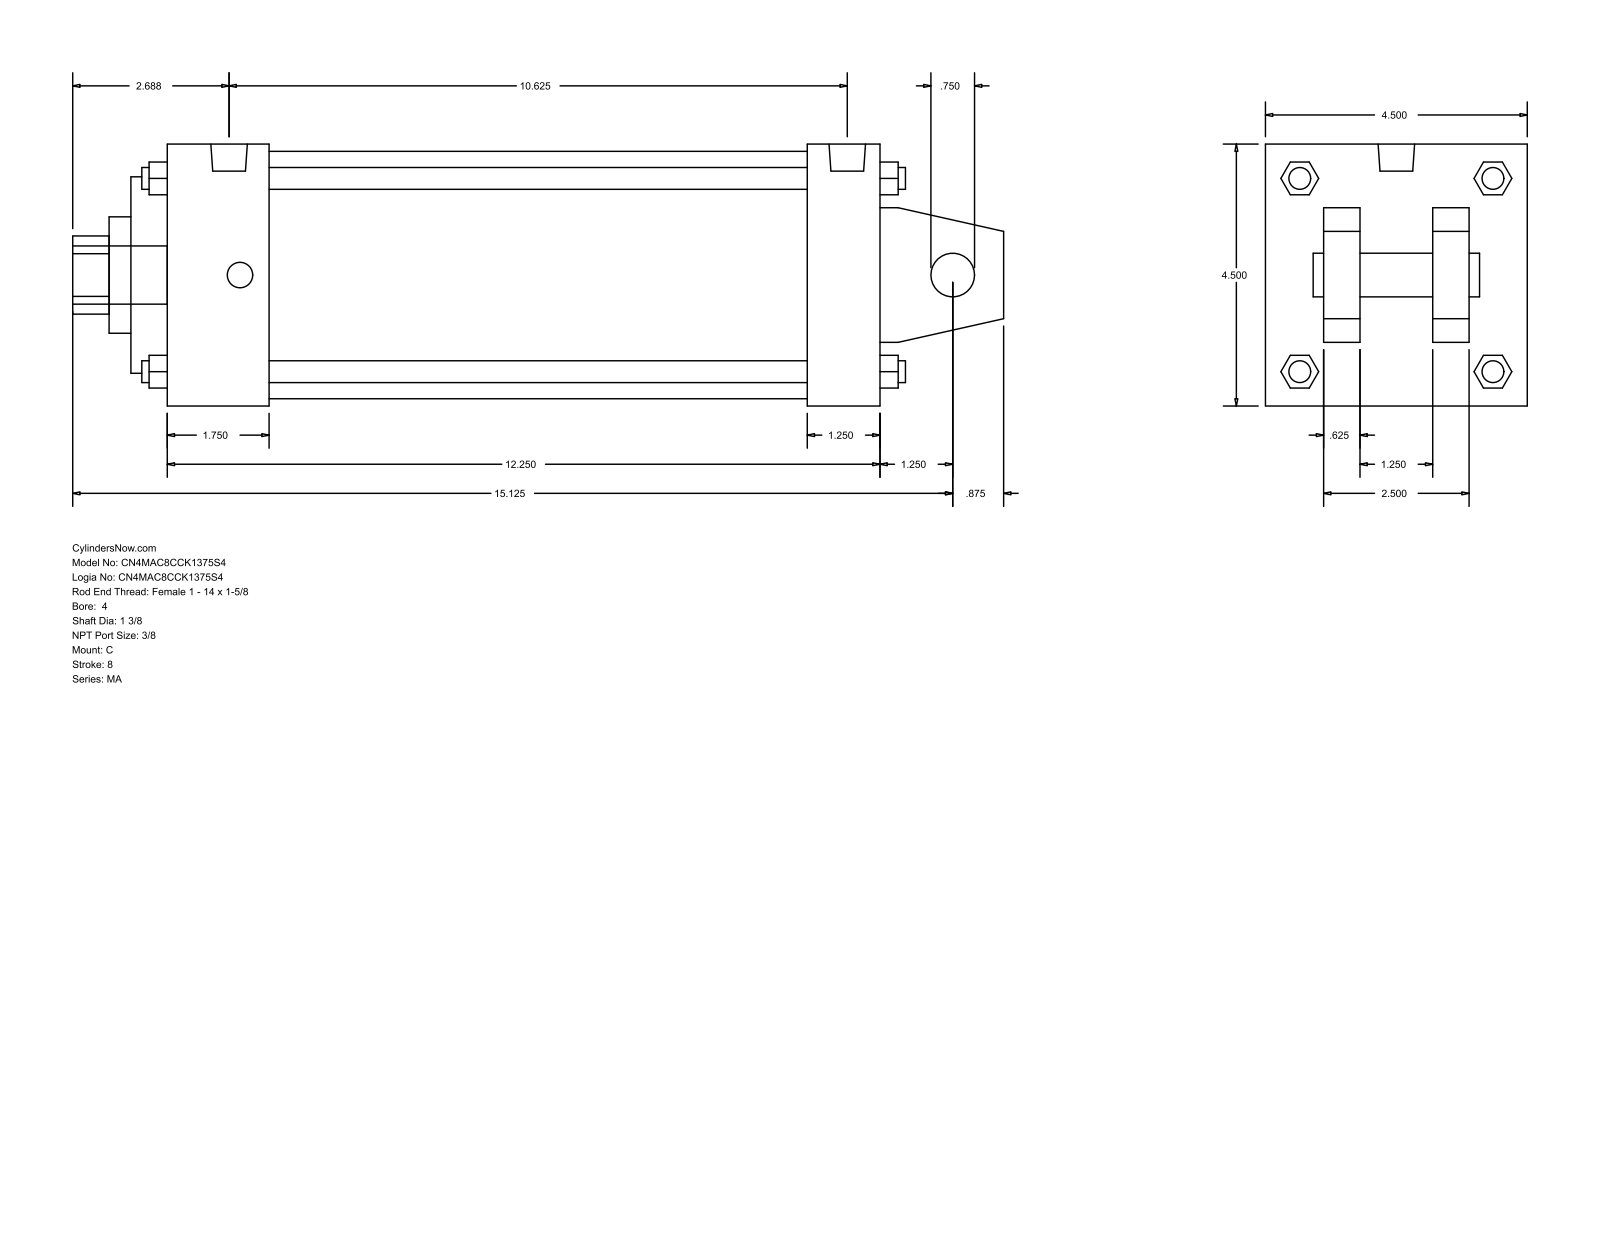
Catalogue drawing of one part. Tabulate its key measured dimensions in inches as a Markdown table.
| quantity | value |
| --- | --- |
| part name | MA_C__0400_1.375 |
| STEP written by | GSSL Pune (CONFIG_CONTROL_DESIGN) |
| units | inches |
| bodies | 0 solids, 141 faces (109 planar, 32 cylindrical, 0 other) |
| overall size | 16 × 4.5 × 4.5 |
| round holes (diameter × count) | 0.75 × 1, 1.375 × 1, 2 × 1, 3.375 × 1, 4.25 × 1 |
| round bosses / shafts (diameter × count) | 0.437 × 4, 0.375 × 4, 0.627 × 2, 1 × 1 |
| partial cylindrical surfaces (radius × count) | 0.672 × 1 |
| main face-to-face distances | 4.5, 0.625, 12.25, 2.875, 1.625, 1, 3.5, 1.875, 12.875, 11.625 |
